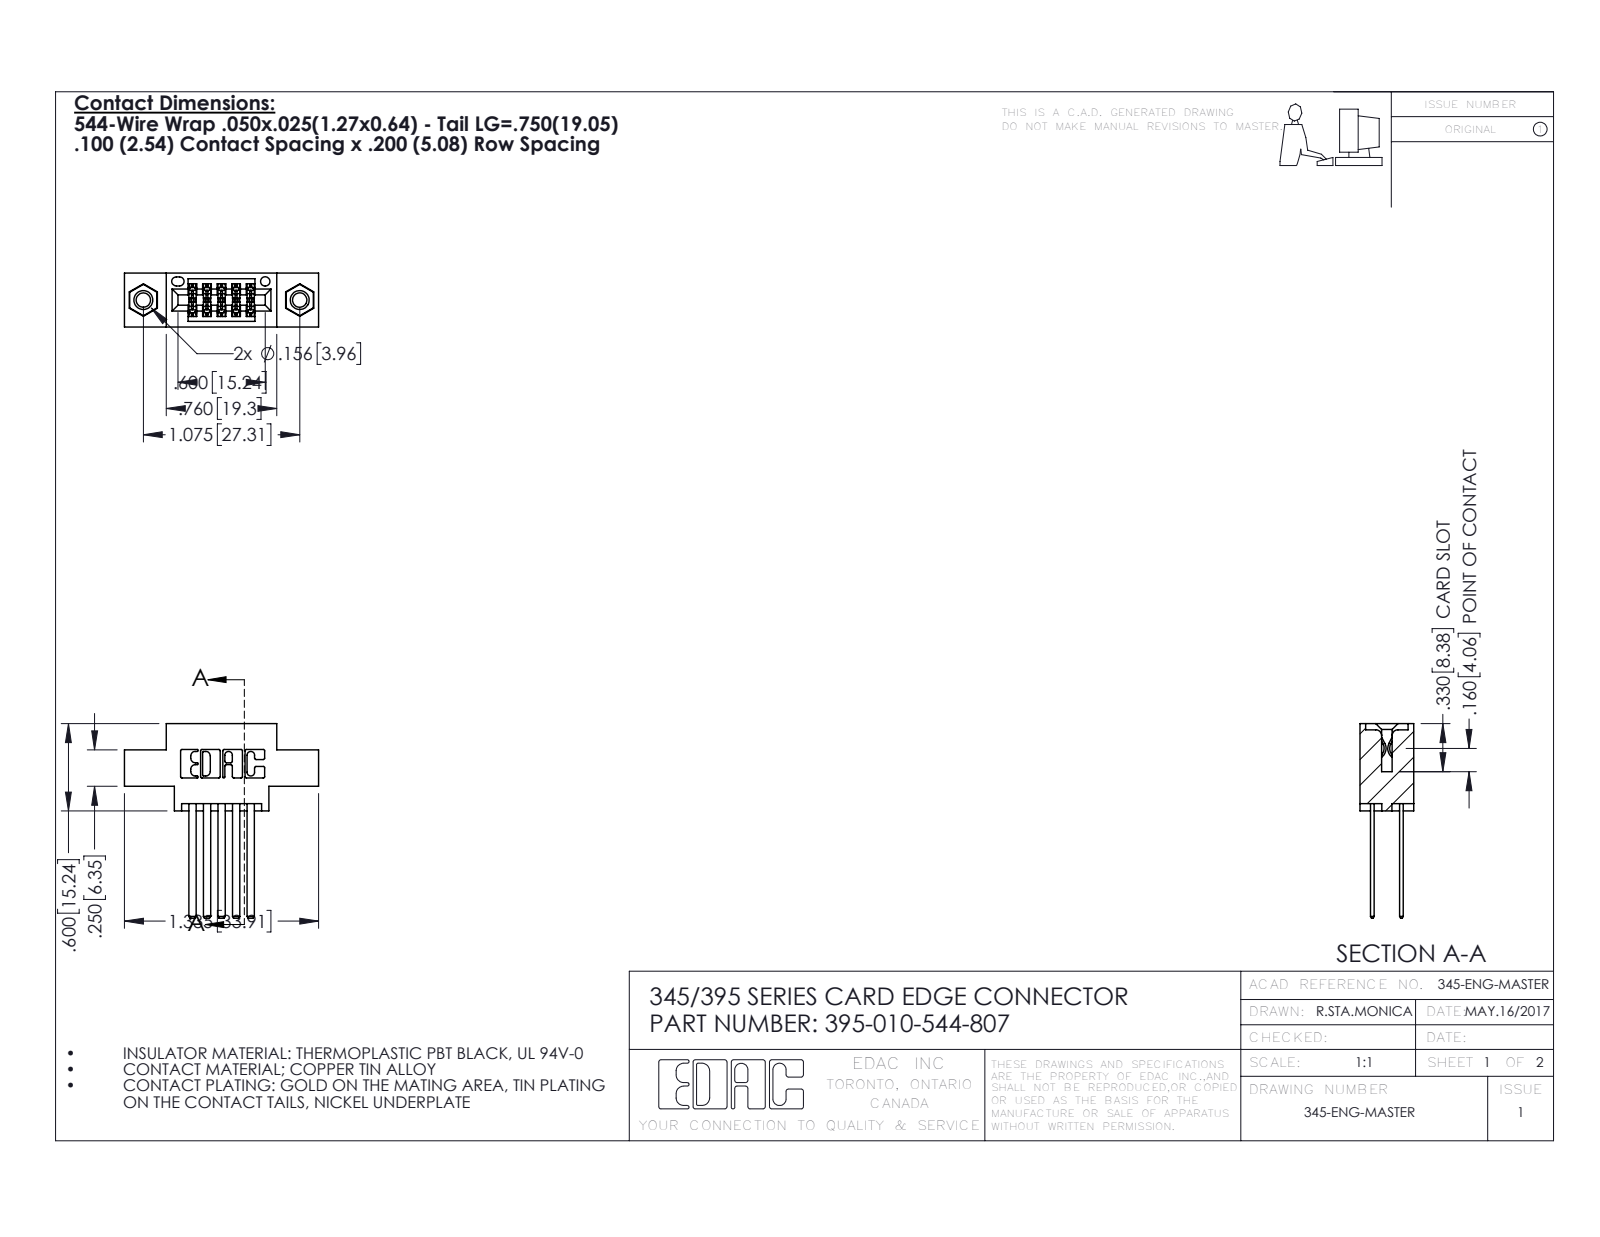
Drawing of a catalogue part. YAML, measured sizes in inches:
part_name: "345-292-001_345-293-144; 345-250-001_345-250-005-103; 345 Part_0.170 Offset - 0.156 Dia-TI; 395-010-544-807"
step_written_by: "SolidWorks 2016 (CONFIG_CONTROL_DESIGN)"
units: inches
bodies: {solids: 13, faces: 630, planar: 406, cylindrical: 208, other: 16}
overall_size: [1.337, 1.335, 0.37]
volume: 0.181
surface_area: 6.582
round_holes:
  - {diameter: 0.098, count: 2}
  - {diameter: 0.125, count: 2}
  - {diameter: 0.156, count: 2}
  - {diameter: 0.064, count: 1}
round_bosses_or_shafts:
  - {diameter: 0.155, count: 2}
partial_cylinders:
  - {radius: 0.01, count: 22}
  - {radius: 0.006, count: 15}
  - {radius: 0.007, count: 6}
  - {radius: 0.031, count: 6}
  - {radius: 0.026, count: 3}
  - {radius: 0.014, count: 2}
  - {radius: 0.019, count: 2}
  - {radius: 0.022, count: 2}
face_to_face_distances: [0.2, 0.072, 0.298, 0.15, 0.098, 0.272, 0.025, 0.37, 0.1, 0.05]
hole_center_spacings: [0.27, 0.847, 1.075]
